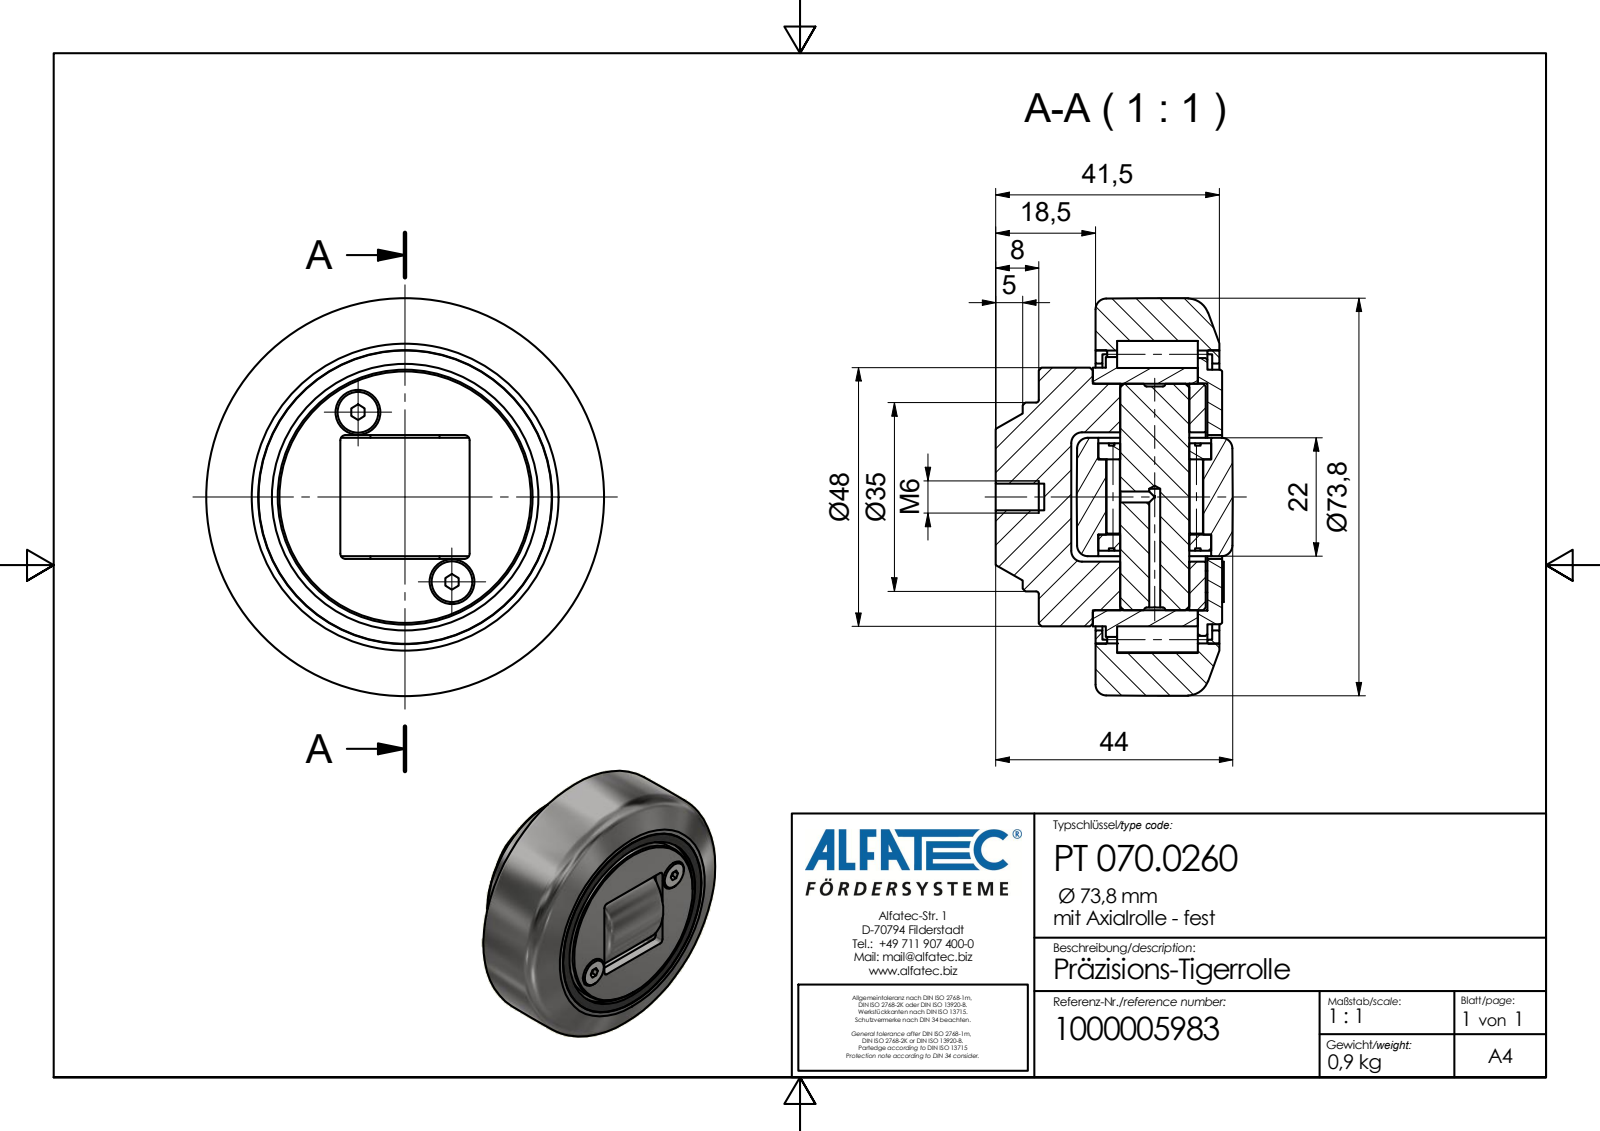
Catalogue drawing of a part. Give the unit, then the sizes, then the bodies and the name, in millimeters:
Units: millimetres
Overall size (bounding box): 73.8 × 73.8 × 44
Round holes (diameter × count): ⌀2 ×2, ⌀4.3 ×2, ⌀2.5 ×1, ⌀3 ×1, ⌀4.92 ×1, ⌀12.8 ×1, ⌀18 ×1, ⌀21 ×1, ⌀42 ×1, ⌀42.2 ×1, ⌀49.5 ×1, ⌀53 ×1
Round bosses / shafts (diameter × count): ⌀7.53 ×2, ⌀4 ×2, ⌀52 ×1, ⌀51.5 ×1, ⌀48 ×1, ⌀47.3 ×1, ⌀41 ×1, ⌀35 ×1
Partial cylindrical surfaces — rounded edges, fillets, slot ends (radius × count): R1 ×4, R2 ×4, R1.5 ×2, R15.5 ×1
Main face-to-face distances: 2.7, 4, 19, 20.8, 23.5, 19.5, 1.8, 23, 0.5, 34
Hole centre spacings: 18, 36
Volume: 99 043 mm³ · Surface area: 36 049 mm²
Bodies: 3 solids, 150 faces (56 planar, 55 cylindrical, 39 other)
Part name (STEP PRODUCT): PT070.0260_Kontur
STEP written by: Autodesk Inventor 2020 (AP242_MANAGED_MODEL_BASED_3D_ENGINEERING_MIM_LF)
